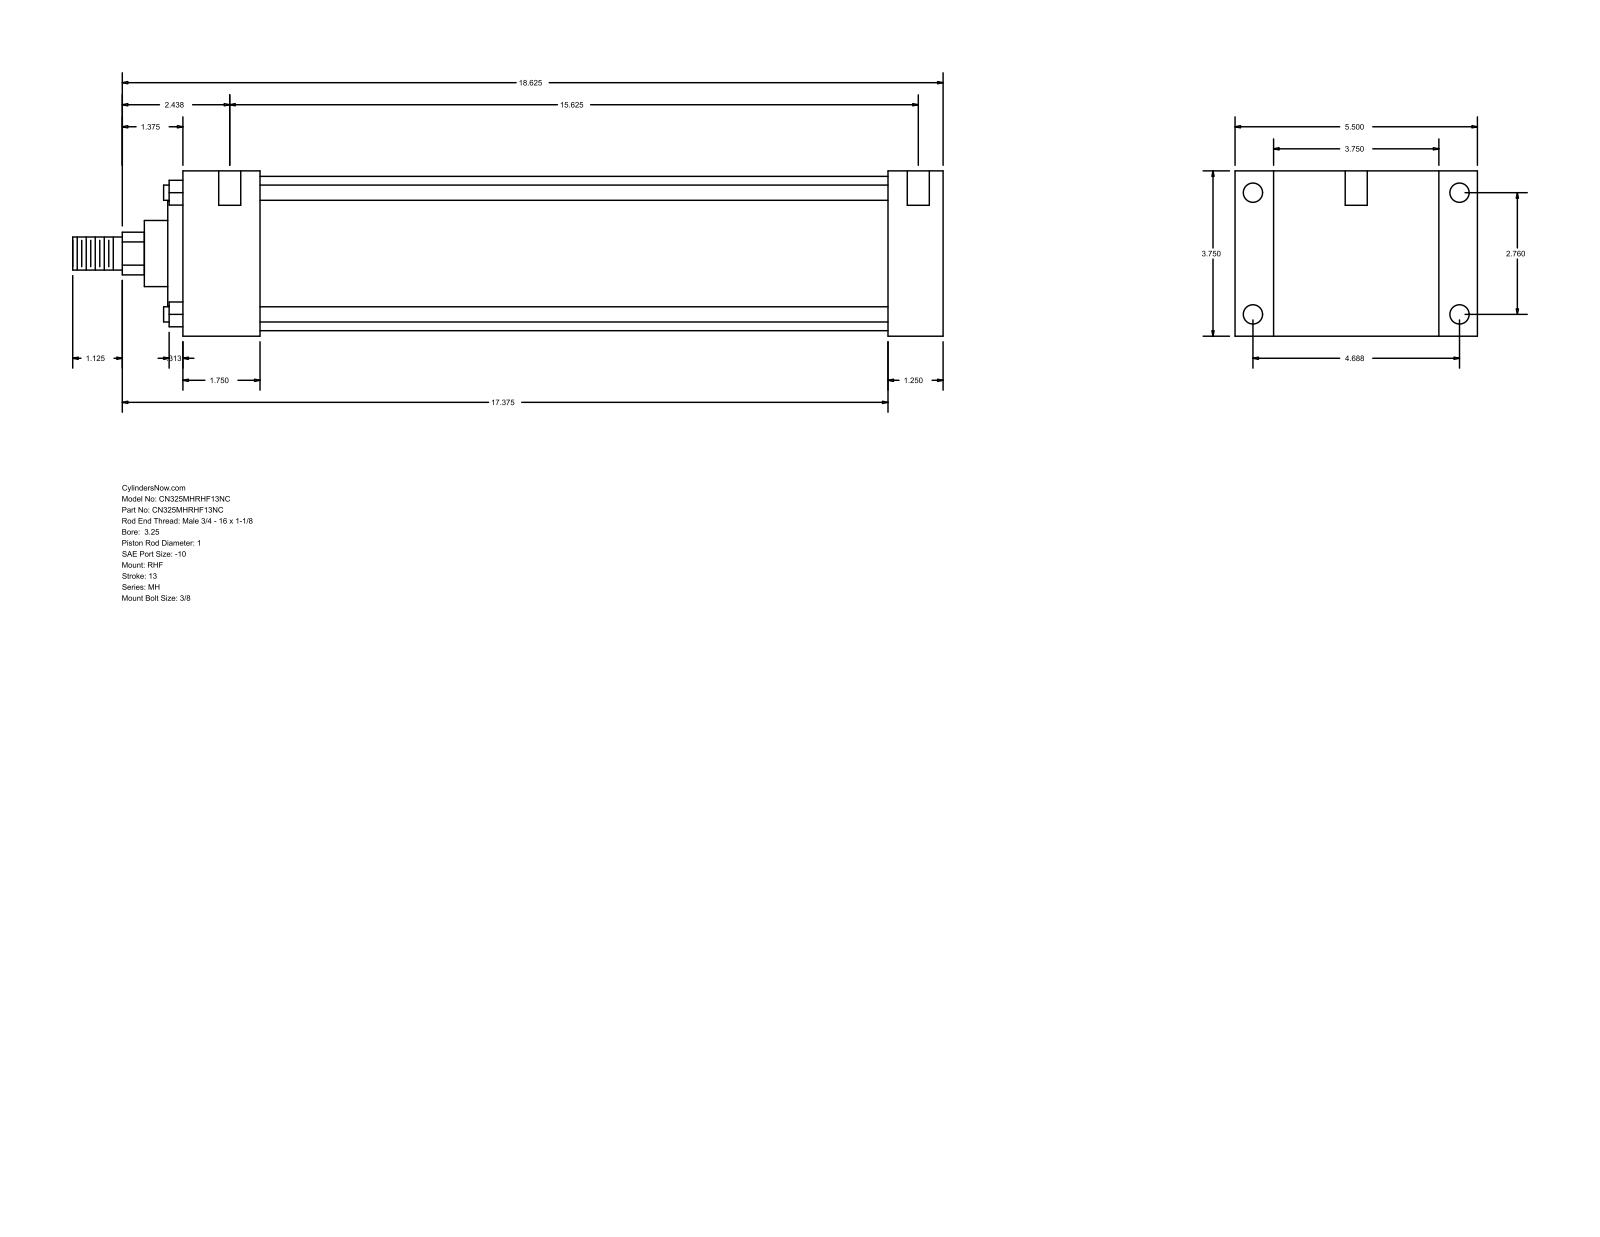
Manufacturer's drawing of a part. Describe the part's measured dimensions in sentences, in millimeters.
The part is named "MH_RHF__0325_1". Its 3-D file was written by "GSSL Pune (CONFIG_CONTROL_DESIGN)". It is 0 solids with 90 faces: 61 planar, 29 cylindrical and 0 other. Overall it measures 501.65 by 139.7 by 95.25 millimeters. Round holes: 4 of diameter 5.56, 4 of diameter 11.13, 2 of diameter 12.7. Round bosses or shafts: 4 of diameter 8.76, 1 of diameter 88.9, 1 of diameter 60.33, 1 of diameter 38.1, 1 of diameter 25.4, 1 of diameter 19.05. Partial cylindrical surfaces (rounded edges, fillets, slot ends): 1 of radius 12.29. The main face-to-face distances are 95.24, 31.75, 22.23, 117.47, 406.4, 438.15, 139.7, 44.46, 361.94, 393.69. The hole center spacings are 70.1, 119.06, 138.16, 403.22, 1.58, 4.76, 396.88, 398.46.
